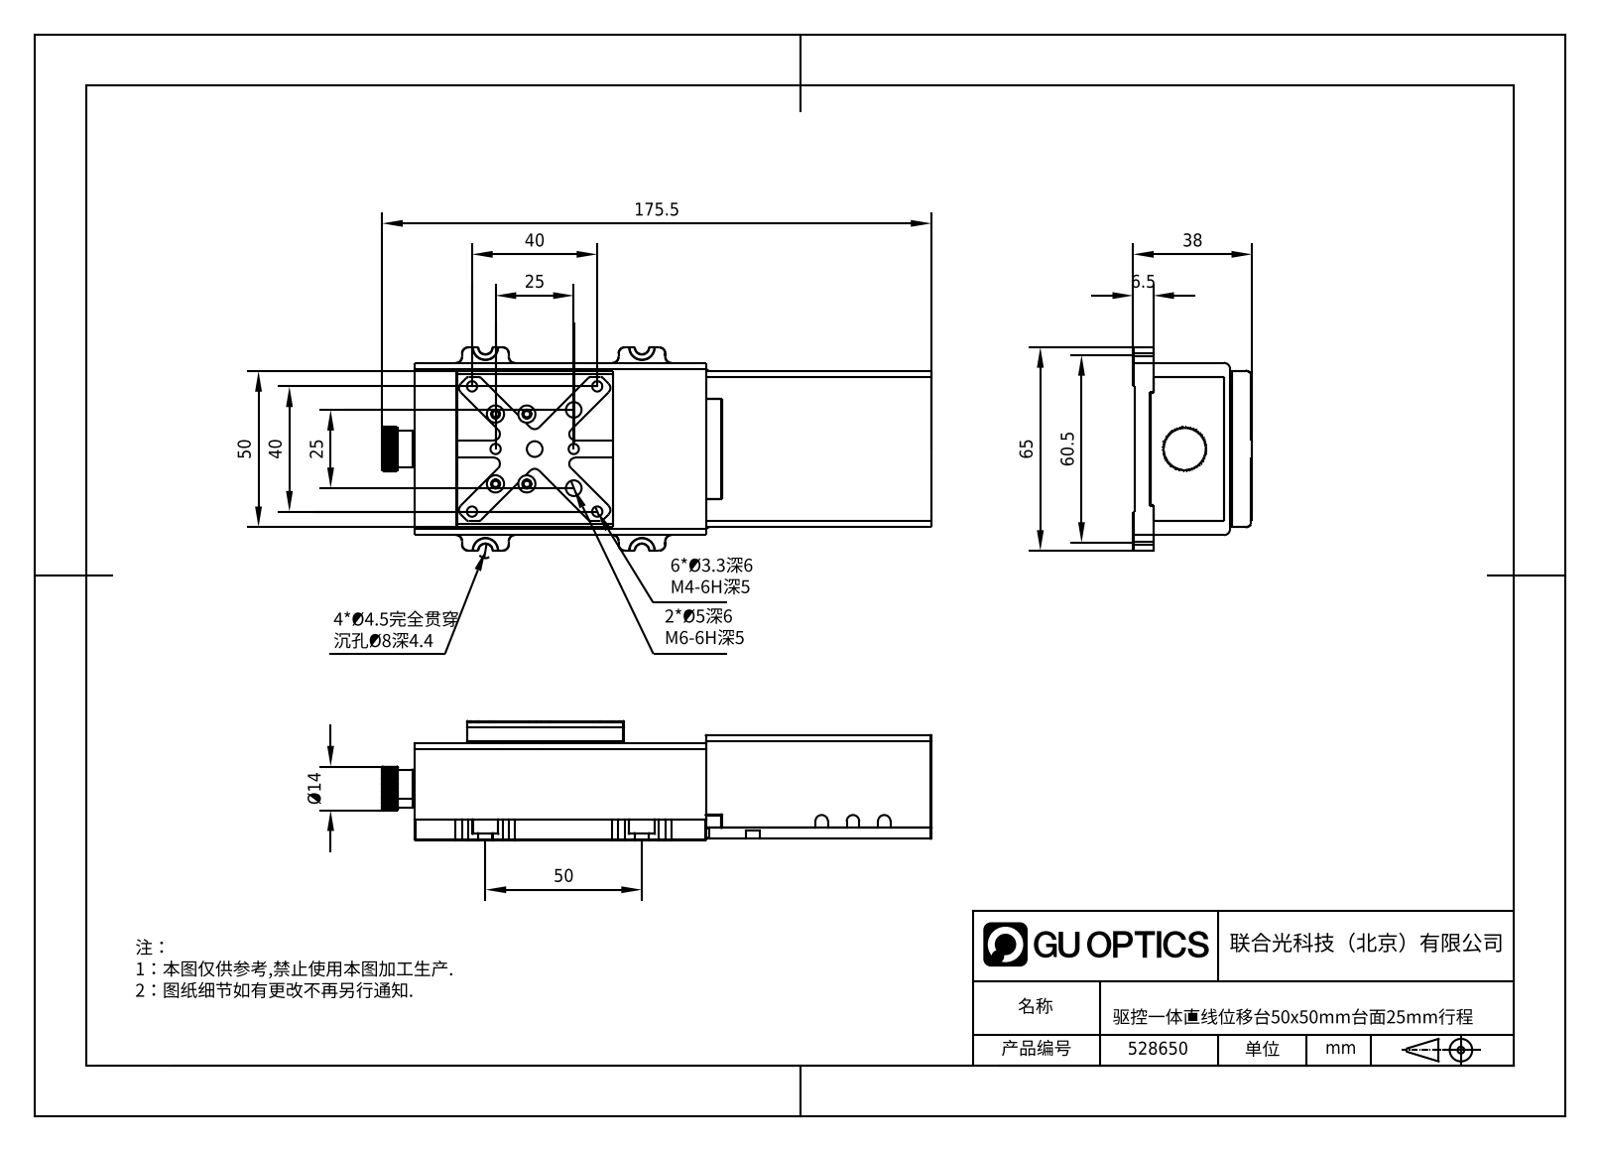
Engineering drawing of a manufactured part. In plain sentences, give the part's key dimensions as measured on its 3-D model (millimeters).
The part is named "528650". Its 3-D file was written by "SolidWorks 2020 (CONFIG_CONTROL_DESIGN)". It is 40 solids with 2768 faces: 1625 planar, 749 cylindrical and 394 other. Overall it measures 175.5 by 65 by 38 millimeters. Its volume is 200 565 cubic millimeters and its surface area 105 485 square millimeters. Round holes: 21 of diameter 2.05, 20 of diameter 2.4, 18 of diameter 2.9, 18 of diameter 5.5, 10 of diameter 1.57, 8 of diameter 1.6, 8 of diameter 2, 8 of diameter 3.6, 8 of diameter 4.4, 6 of diameter 3.3, 4 of diameter 5, 3 of diameter 2.5. Round bosses or shafts: 4 of diameter 2.2, 4 of diameter 2, 1 of diameter 22, 1 of diameter 13, 1 of diameter 12, 1 of diameter 3. Partial cylindrical surfaces (rounded edges, fillets, slot ends): 41 of radius 2, 26 of radius 1, 16 of radius 0.1, 8 of radius 0.32, 6 of radius 0.23, 4 of radius 1.3, 4 of radius 2.2, 4 of radius 2.2. The main face-to-face distances are 2.5, 2, 4, 4.5, 1, 30.5, 5, 28, 6, 1.5. The hole center spacings are 30.8, 15, 34.26, 4.21, 4.51, 6.65, 7.07, 8.
